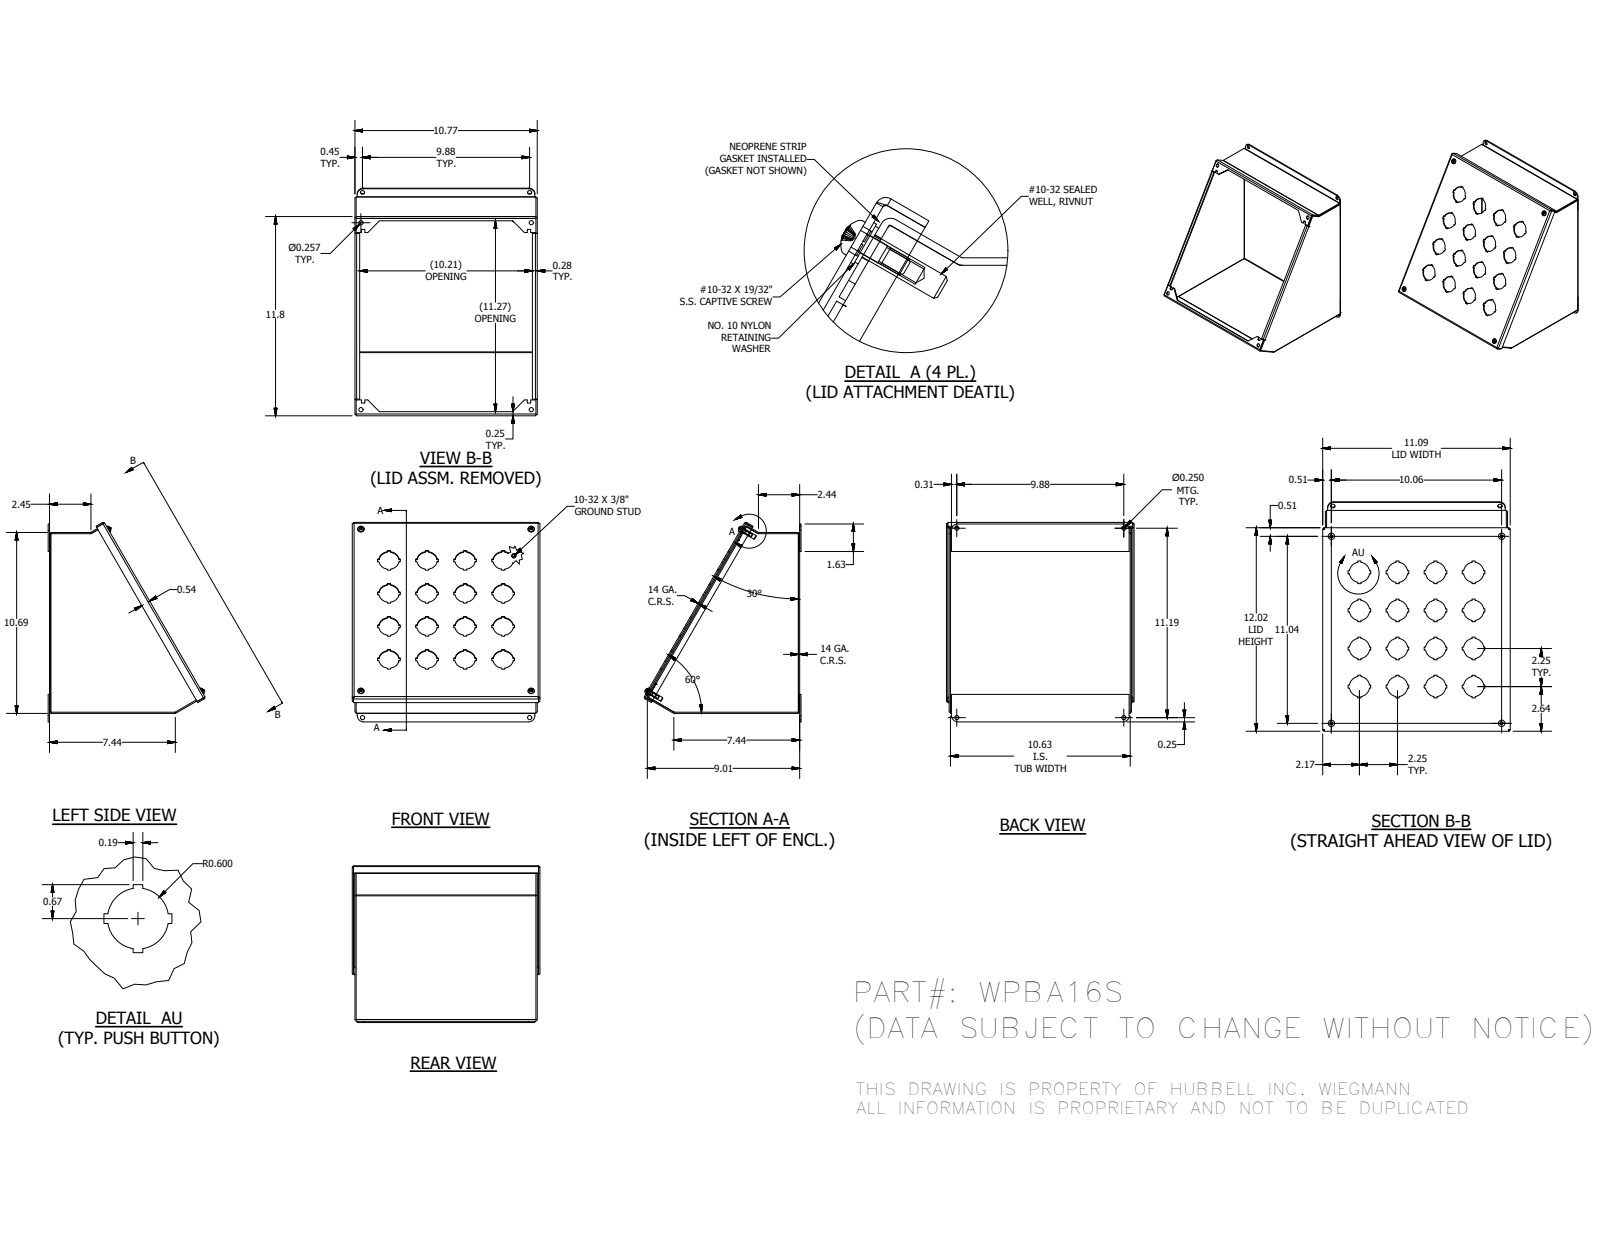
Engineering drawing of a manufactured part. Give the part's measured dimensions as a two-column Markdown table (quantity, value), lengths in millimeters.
| quantity | value |
| --- | --- |
| part name | WPBA16SBKP; WPBA4ROWEWPR; WPBA4ROWEWPL; 34984 (+6 more) |
| STEP written by | Autodesk Inventor 2014 (AUTOMOTIVE_DESIGN) |
| units | millimeters |
| bodies | 19 solids, 736 faces (483 planar, 154 cylindrical, 99 other) |
| overall size | 299.29 × 281.61 × 235.35 |
| volume | 677 538 mm³ |
| surface area | 738 011 mm² |
| round holes (diameter × count) | 30.48 × 16, 3.96 × 4, 4.98 × 4, 6.35 × 4, 6.53 × 4, 7.06 × 4, 7.14 × 4 |
| round bosses / shafts (diameter × count) | 4.83 × 5, 11.51 × 4, 10.31 × 4, 9.47 × 4, 6.3 × 4, 6.35 × 1 |
| partial cylindrical surfaces (radius × count) | 0.79 × 12, 2.67 × 12, 2.27 × 4, 9.53 × 4 |
| main face-to-face distances | 1.88, 269.88, 271.76, 273.63, 271.75, 1.87, 269.65, 3.76, 267.77, 271.53 |
| hole center spacings | 127.79, 57.15, 80.82, 114.3, 171.45, 180.73, 80.83, 206.06 |
